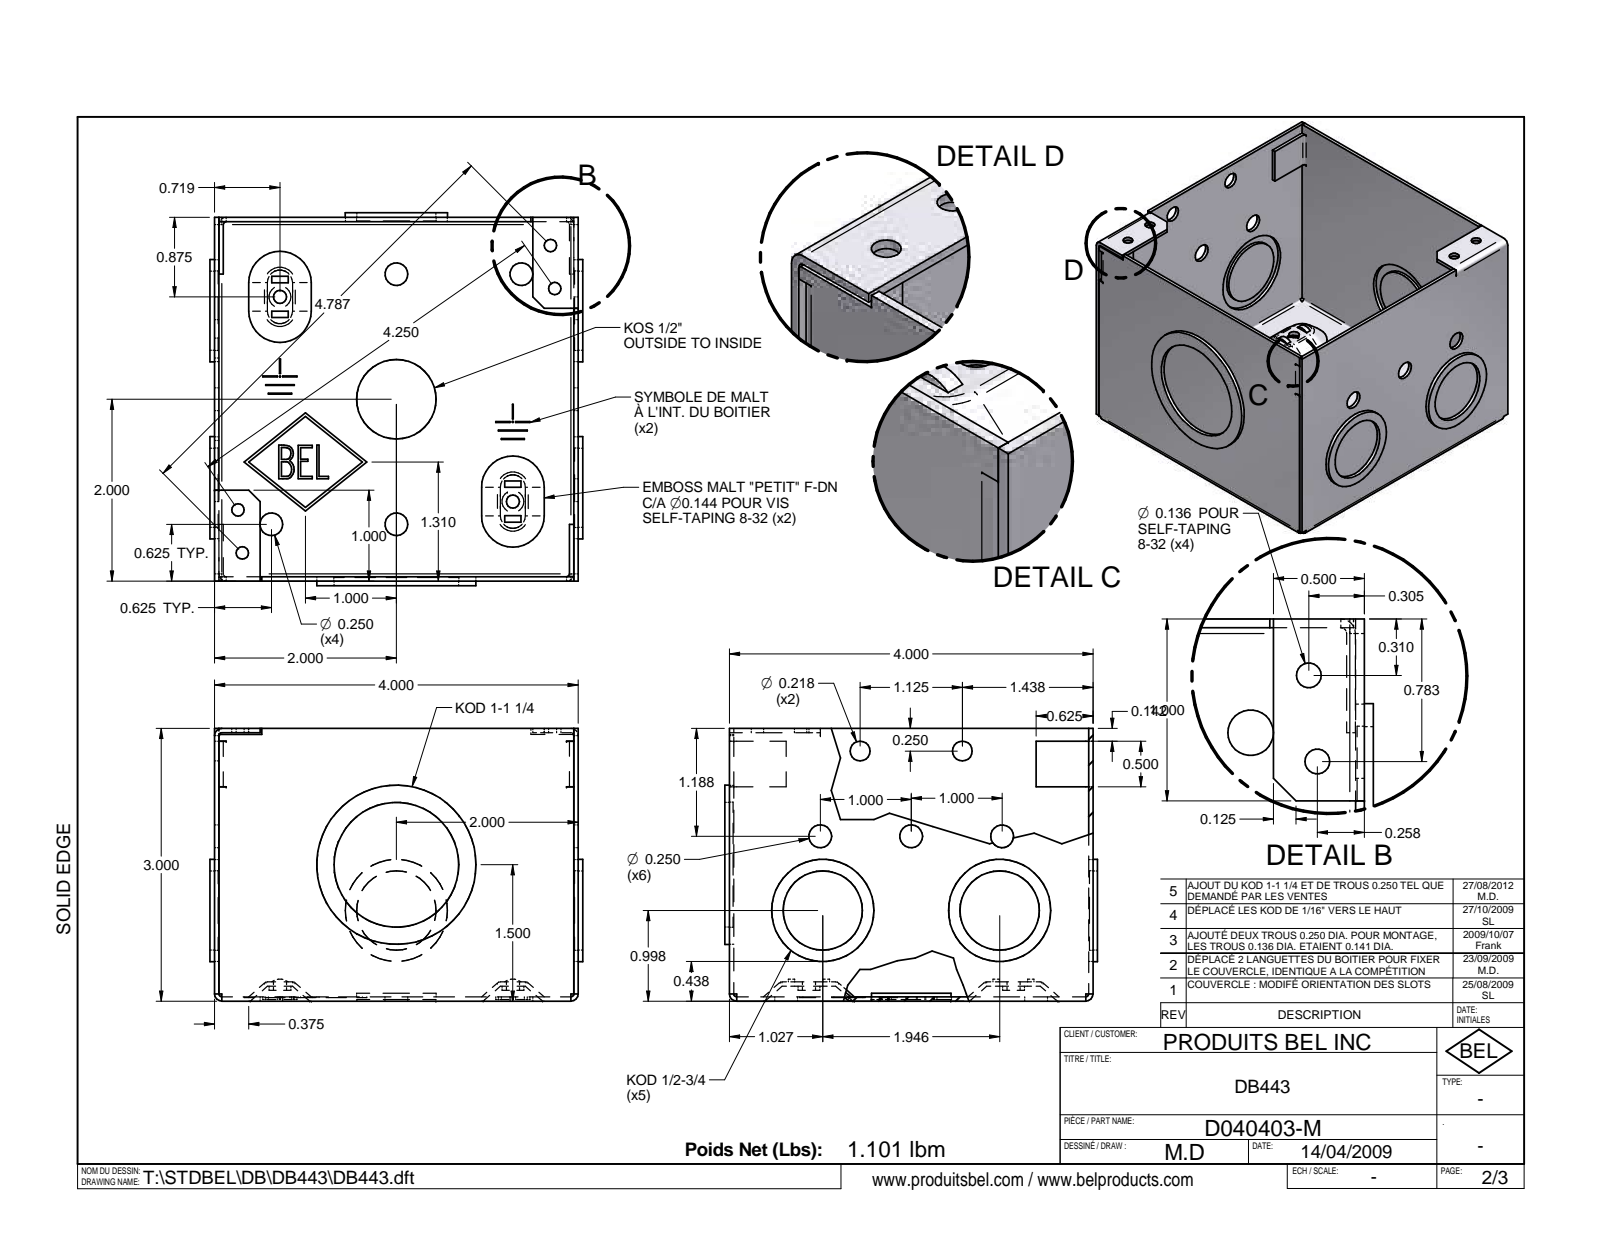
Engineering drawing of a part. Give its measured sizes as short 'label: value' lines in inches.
name: DB443B; DB443C
written by: Unknown (AUTOMOTIVE_DESIGN)
unit: in
bodies: 2 solids, 357 faces (252 planar, 82 cylindrical, 23 other)
size: 4.1 × 4.1 × 3.048
volume: 3.83 in³; area: 168.2 in²
holes: 7× ⌀0.25, 4× ⌀0.136, 4× ⌀0.87, 3× ⌀1.12, 2× ⌀0.014, 2× ⌀0.144, 2× ⌀0.218, 1× ⌀1.37, 1× ⌀1.748
bosses: 4× ⌀0.875, 3× ⌀1.125, 2× ⌀0.24, 1× ⌀1.751, 1× ⌀1.375
rounds: 10× R0.032, 10× R0.08, 8× R0.048, 2× R0.1, 2× R0.145
face distances: 0.048, 3.952, 3, 4, 3.904, 2.952, 3.048, 0.04, 3.96, 3.912
hole spacings: 1.305, 1.375, 1.705, 0.4, 0.449, 0.476, 0.815, 0.875
